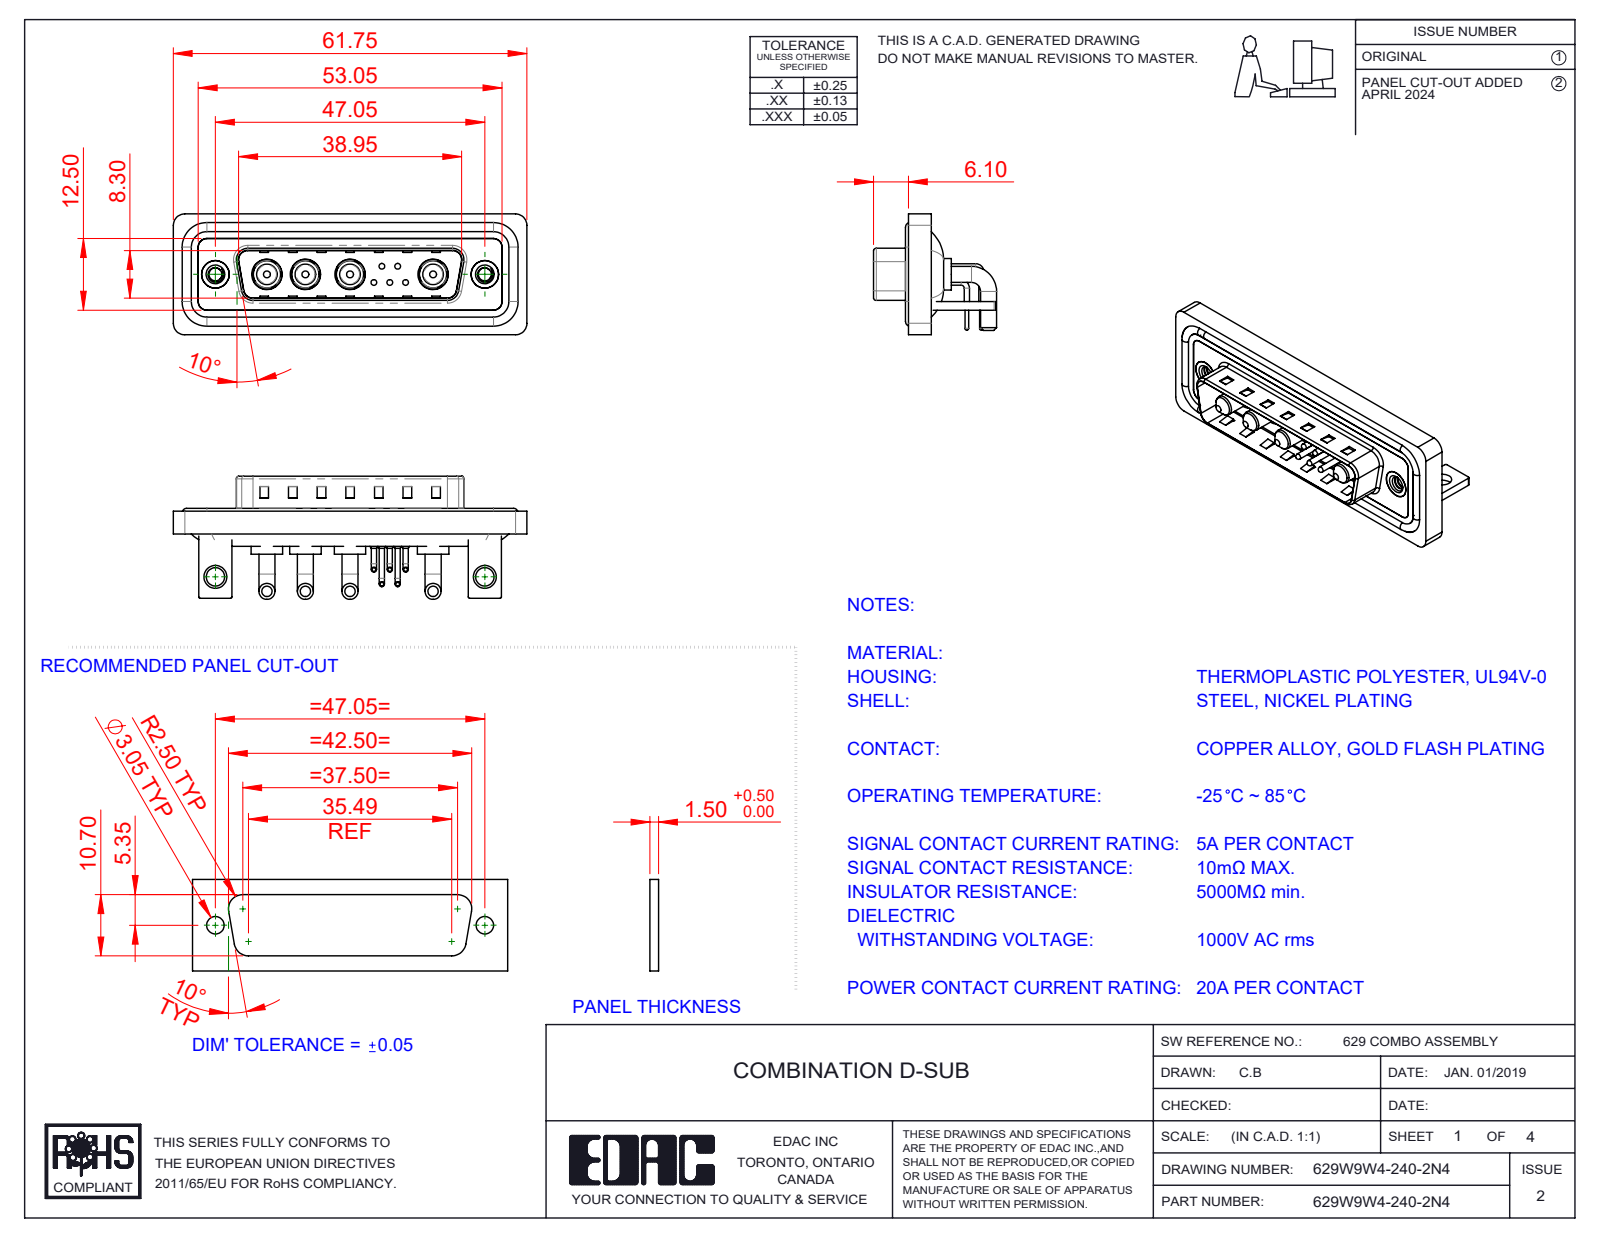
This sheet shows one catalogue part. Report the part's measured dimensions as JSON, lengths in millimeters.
{"part_name": "629Combo Housing_9W4; 629W9W4-140-2N4; Power Pin_20A RA; 629Combo Shell Front_25 Contacts (+6 more)", "step_written_by": "SolidWorks 2023 (CONFIG_CONTROL_DESIGN)", "units": "millimeters", "bodies": {"solids": 22, "faces": 1245, "planar": 589, "cylindrical": 470, "other": 186}, "overall_size": [61.75, 21.5, 21.1], "volume_mm3": 7982, "surface_area_mm2": 12963, "round_holes": [[0.75, 5], [1.6, 5], [2, 5], [4.85, 4], [5.3, 4], [2.26, 2], [3.2, 2], [4, 2], [4.8, 2], [5, 2]], "round_bosses_or_shafts": [[0.9, 10], [2.8, 8], [1.5, 5], [1, 5], [0.65, 5], [5.5, 4], [5.2, 4], [4.75, 4]], "partial_cylinders_radius": [[2, 19], [1.5, 18], [0.25, 16], [0.5, 9], [1.6, 8], [1.01, 5], [0.6, 4], [0.65, 4]], "face_to_face_distances": [0.4, 1.5, 0.8, 2.9, 2.1, 1.1, 3.7, 4.1, 4.5, 1.6], "hole_center_spacings": [3.16, 2.77, 5.04, 14.5, 47.05, 2.78, 4.4, 4.41]}
